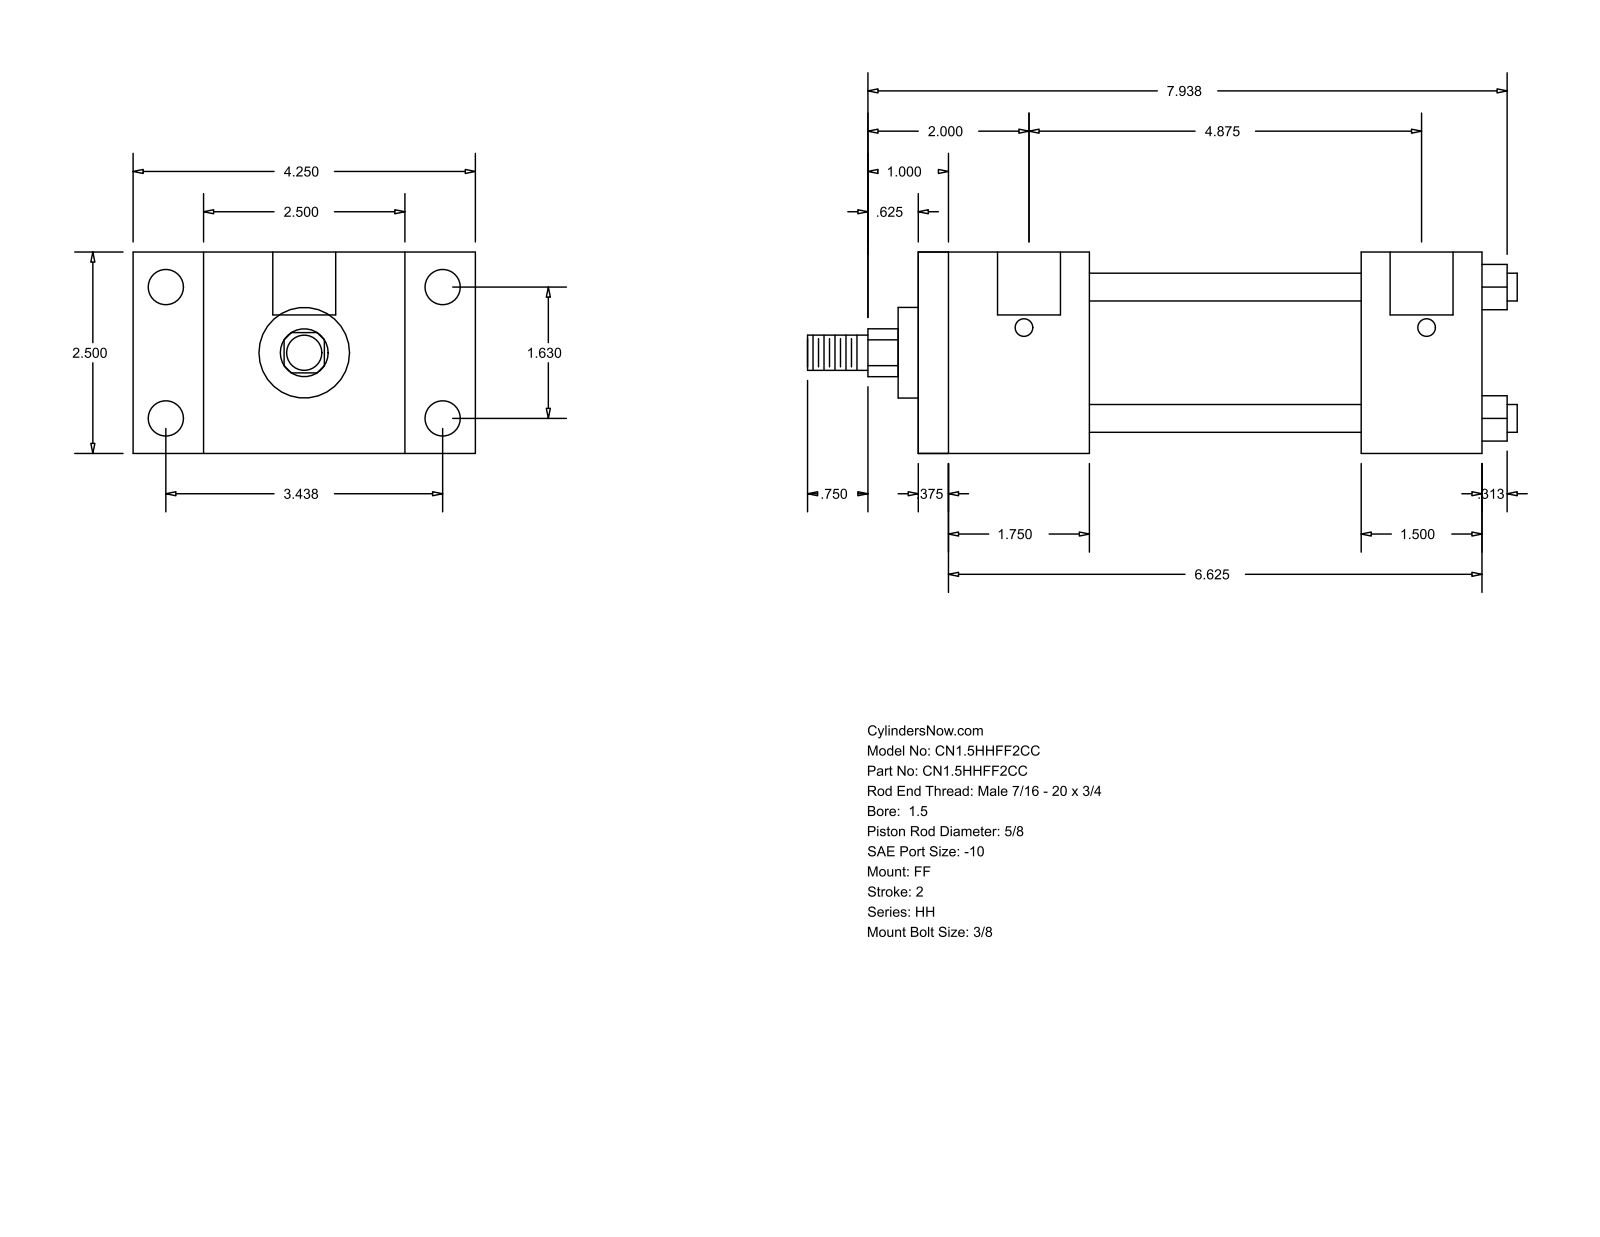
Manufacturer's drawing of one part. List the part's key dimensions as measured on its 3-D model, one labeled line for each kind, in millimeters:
Part name (STEP PRODUCT): HH_FF__0150_0.625
STEP written by: GSSL Pune (CONFIG_CONTROL_DESIGN)
Units: millimetres
Bodies: 0 solids, 92 faces (64 planar, 28 cylindrical, 0 other)
Overall size (bounding box): 223.84 × 107.95 × 63.5
Round holes (diameter × count): ⌀5.56 ×4, ⌀11.13 ×4, ⌀19.84 ×2
Round bosses / shafts (diameter × count): ⌀8.76 ×4, ⌀44.45 ×1, ⌀28.57 ×1, ⌀15.88 ×1, ⌀11.11 ×1
Partial cylindrical surfaces — rounded edges, fillets, slot ends (radius × count): R7.54 ×1
Main face-to-face distances: 63.5, 177.8, 9.52, 168.28, 44.45, 53.97, 123.83, 139.69, 130.17, 85.72
Hole centre spacings: 1.59, 41.4, 87.32, 96.64, 125.41, 127, 123.82
